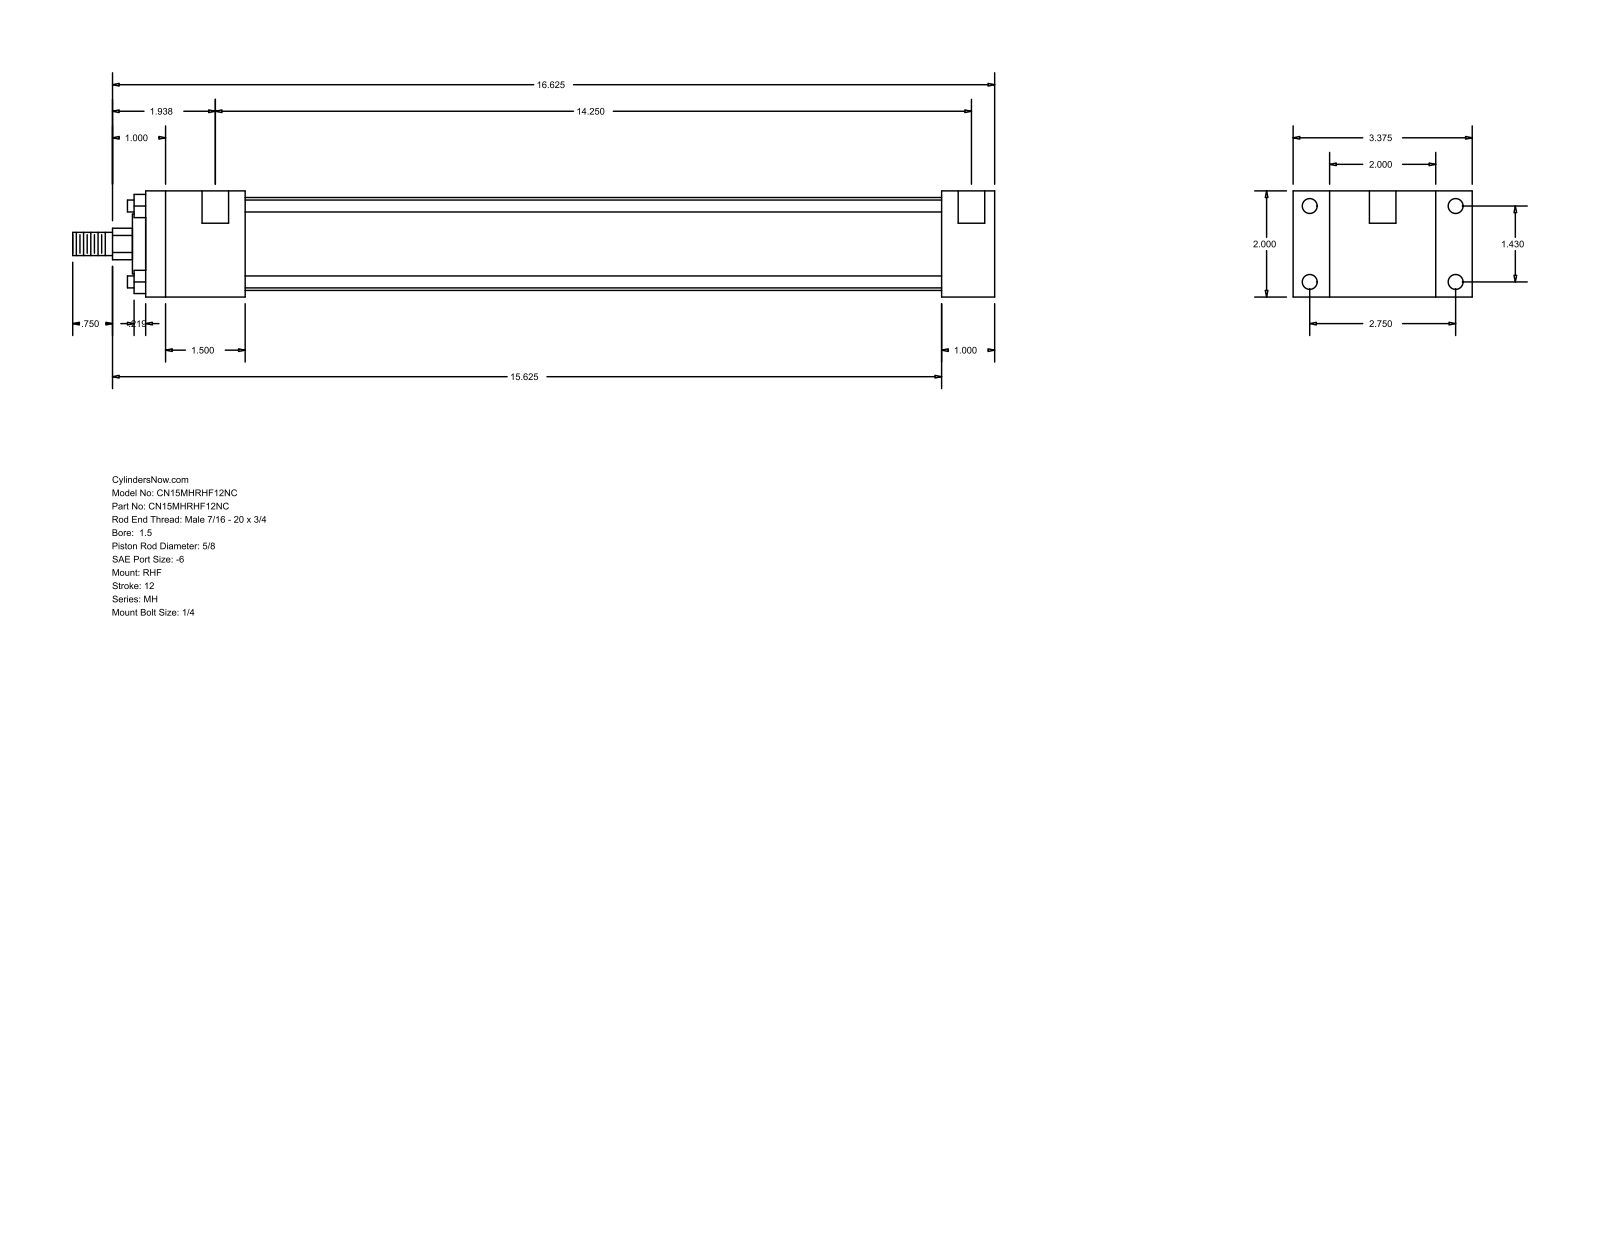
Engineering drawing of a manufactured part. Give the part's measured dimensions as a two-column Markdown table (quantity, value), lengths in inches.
| quantity | value |
| --- | --- |
| part name | MH_RHF__0150_0.625 |
| STEP written by | GSSL Pune (CONFIG_CONTROL_DESIGN) |
| units | inches |
| bodies | 0 solids, 88 faces (60 planar, 28 cylindrical, 0 other) |
| overall size | 17.375 × 3.375 × 2 |
| round holes (diameter × count) | 0.219 × 4, 0.281 × 4, 0.5 × 2 |
| round bosses / shafts (diameter × count) | 0.225 × 4, 1.75 × 1, 1.125 × 1, 0.625 × 1, 0.437 × 1 |
| partial cylindrical surfaces (radius × count) | 0.297 × 1 |
| main face-to-face distances | 2, 0.687, 2.687, 1, 15, 16, 3.375, 1.875, 13.125, 14.125 |
| hole center spacings | 1.43, 2.75, 3.099, 14.375, 0.125, 14.25 |
